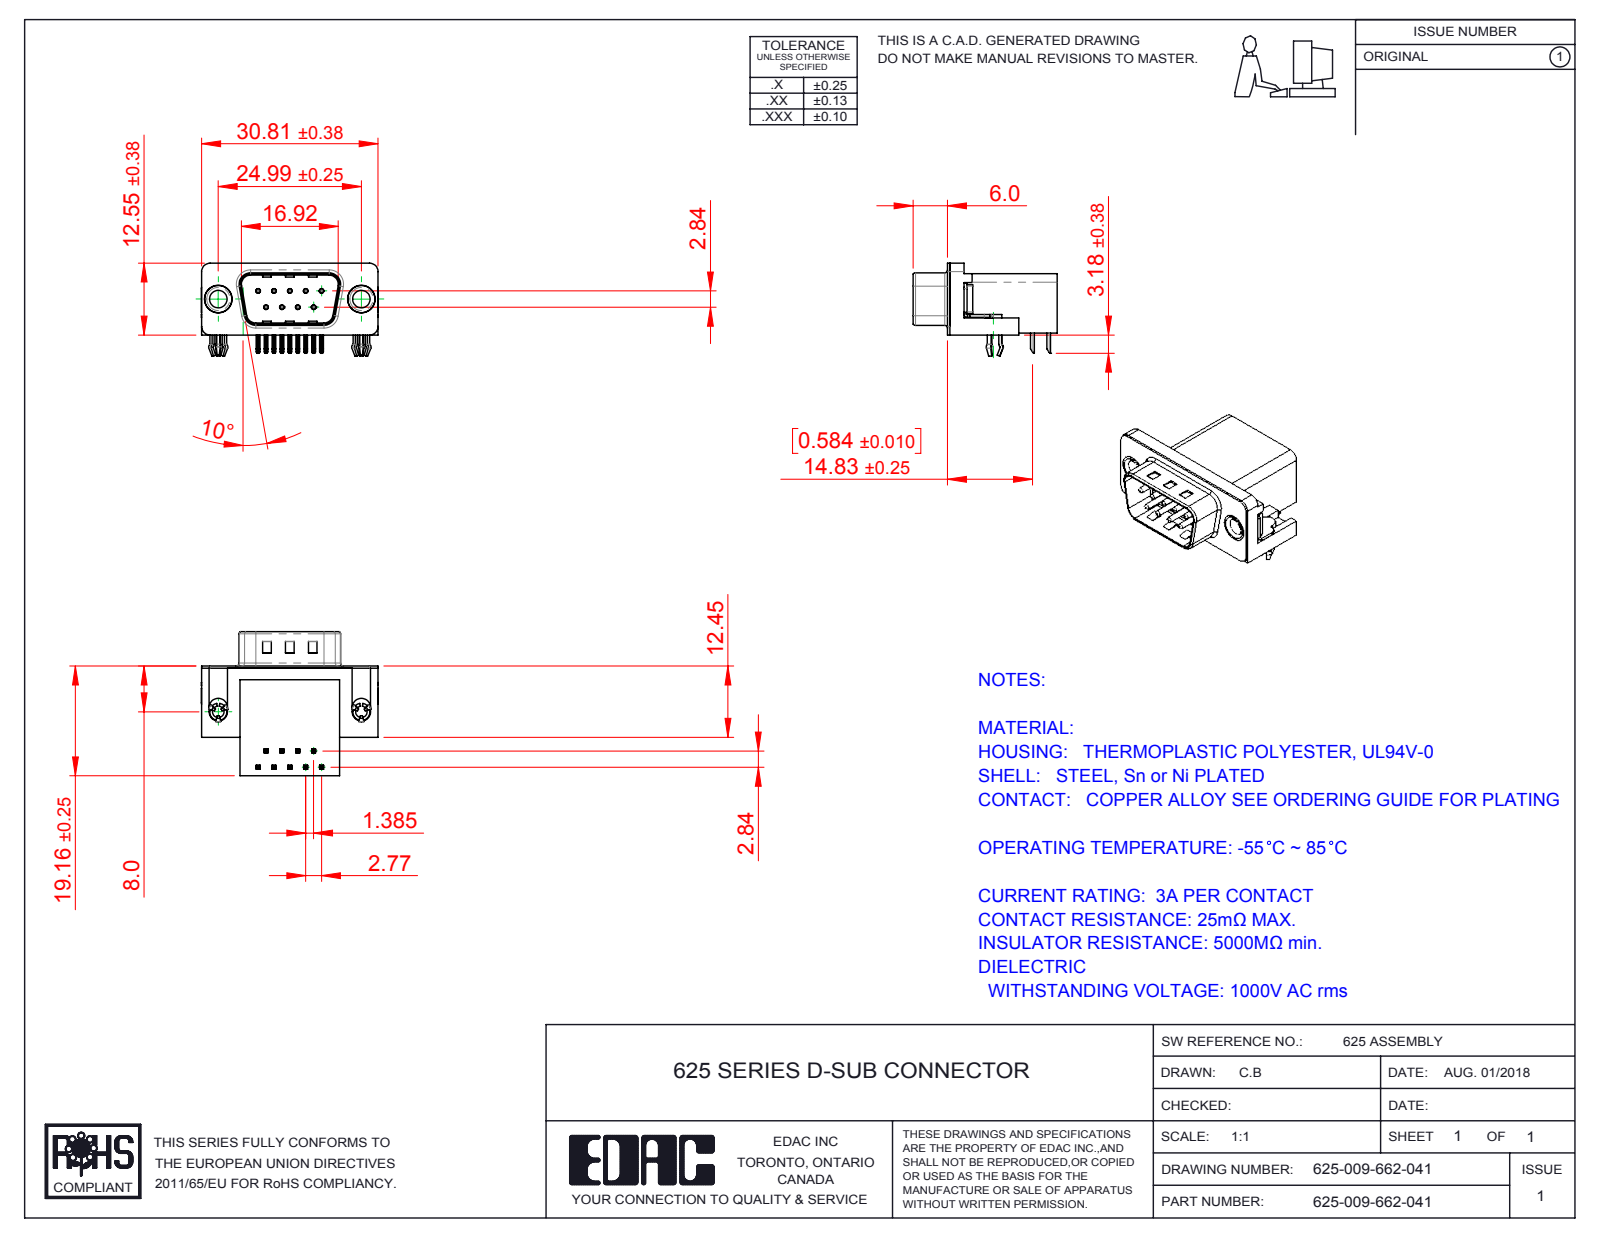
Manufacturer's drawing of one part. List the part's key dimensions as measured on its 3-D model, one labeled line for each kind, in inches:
Part name (STEP PRODUCT): 625 3 Prong Board Lock; 625 Contact Top; 625 Thru Hole Rivet; 625 Shell_9 Socket (+3 more)
STEP written by: SolidWorks 2016 (CONFIG_CONTROL_DESIGN)
Units: inches
Bodies: 15 solids, 1057 faces (611 planar, 305 cylindrical, 141 other)
Overall size (bounding box): 1.216 × 0.991 × 0.64
Volume: 0.273 in³ · Surface area: 7.733 in²
Round holes (diameter × count): ⌀0.014 ×9, ⌀0.031 ×9, ⌀0.079 ×2, ⌀0.12 ×2, ⌀0.157 ×2, ⌀0.189 ×2, ⌀0.197 ×2
Round bosses / shafts (diameter × count): ⌀0.03 ×9, ⌀0.193 ×2, ⌀0.187 ×2, ⌀0.152 ×2, ⌀0.118 ×2
Partial cylindrical surfaces — rounded edges, fillets, slot ends (radius × count): R0.01 ×48, R0.005 ×18, R0.039 ×16, R0.02 ×9, R0.059 ×8, R0.063 ×8, R0.035 ×4, R0.079 ×4
Main face-to-face distances: 0.016, 0.407, 0.739, 0.754, 0.114, 0.64, 0.098, 0.014, 0.421, 0.264
Hole centre spacings: 0.124, 0.109, 0.218, 0.198, 0.198, 0.327, 0.294, 0.295
